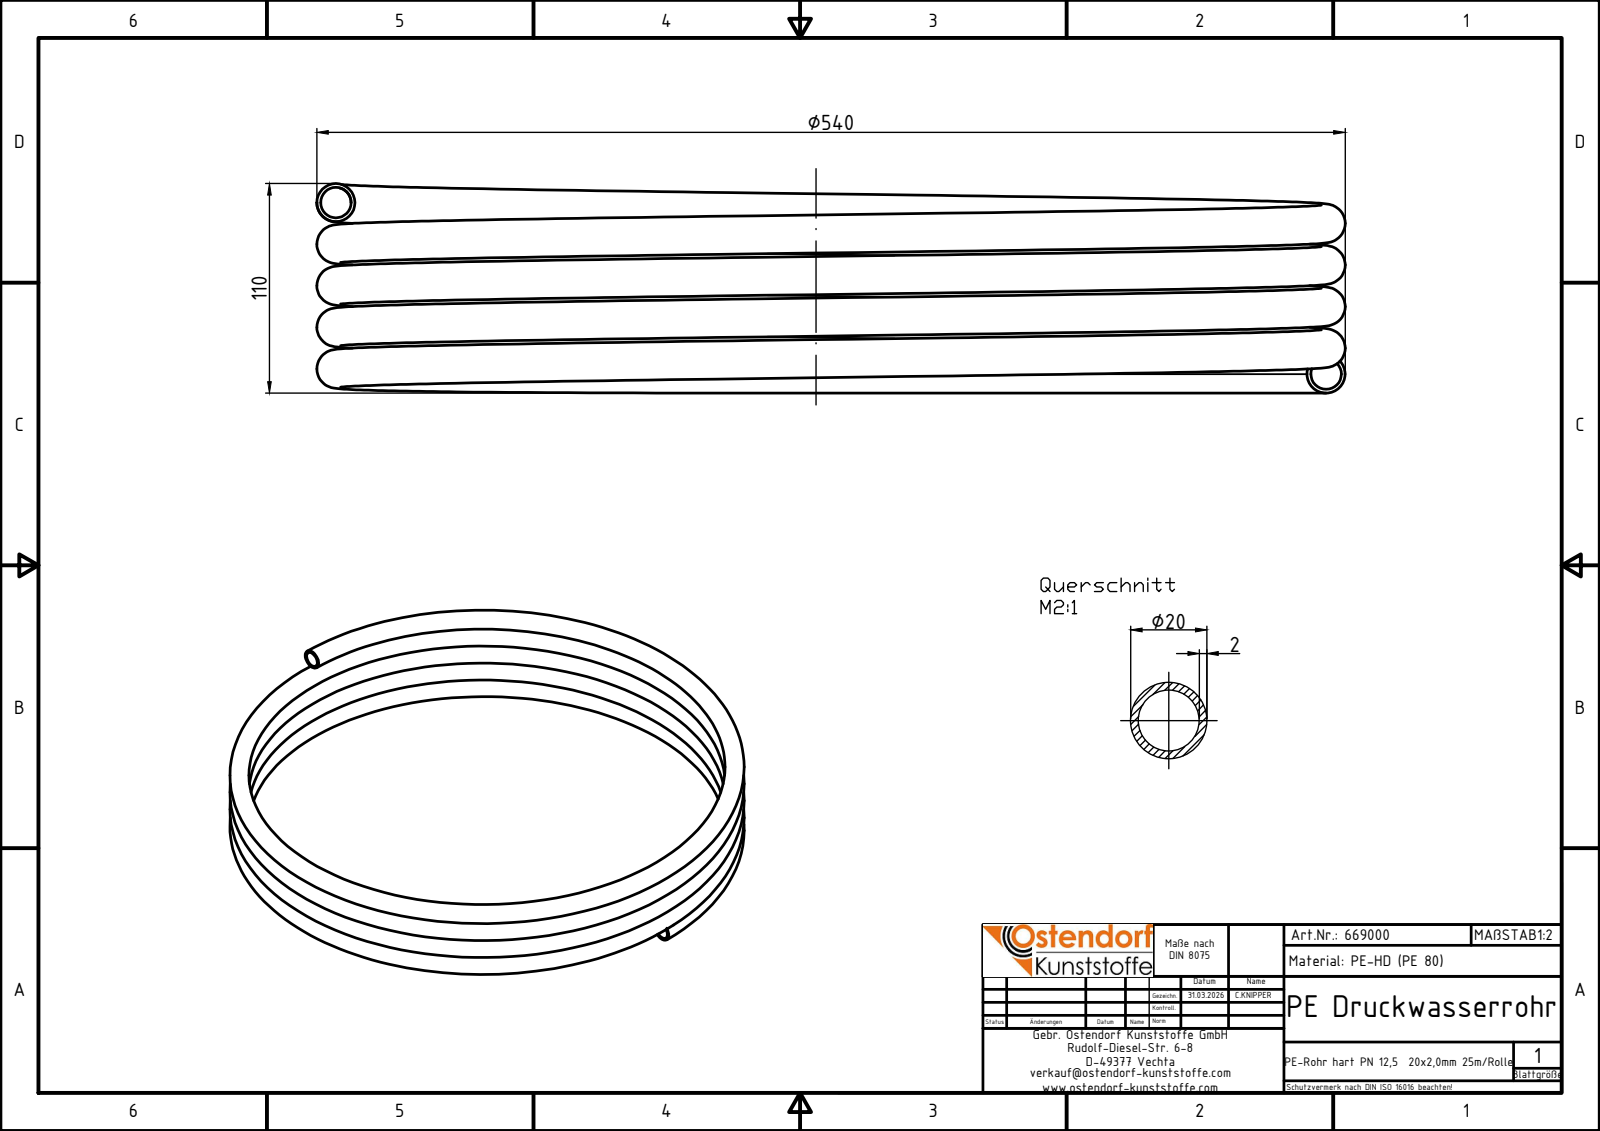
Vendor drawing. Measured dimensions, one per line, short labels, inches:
name: 669000z
written by: Autodesk Inventor 2024 (AUTOMOTIVE_DESIGN)
unit: in
bodies: 1 solid, 7 faces (3 planar, 0 cylindrical, 4 other)
size: 21.26 × 21.26 × 4.331
volume: 50.11 in³; area: 1 270 in²
